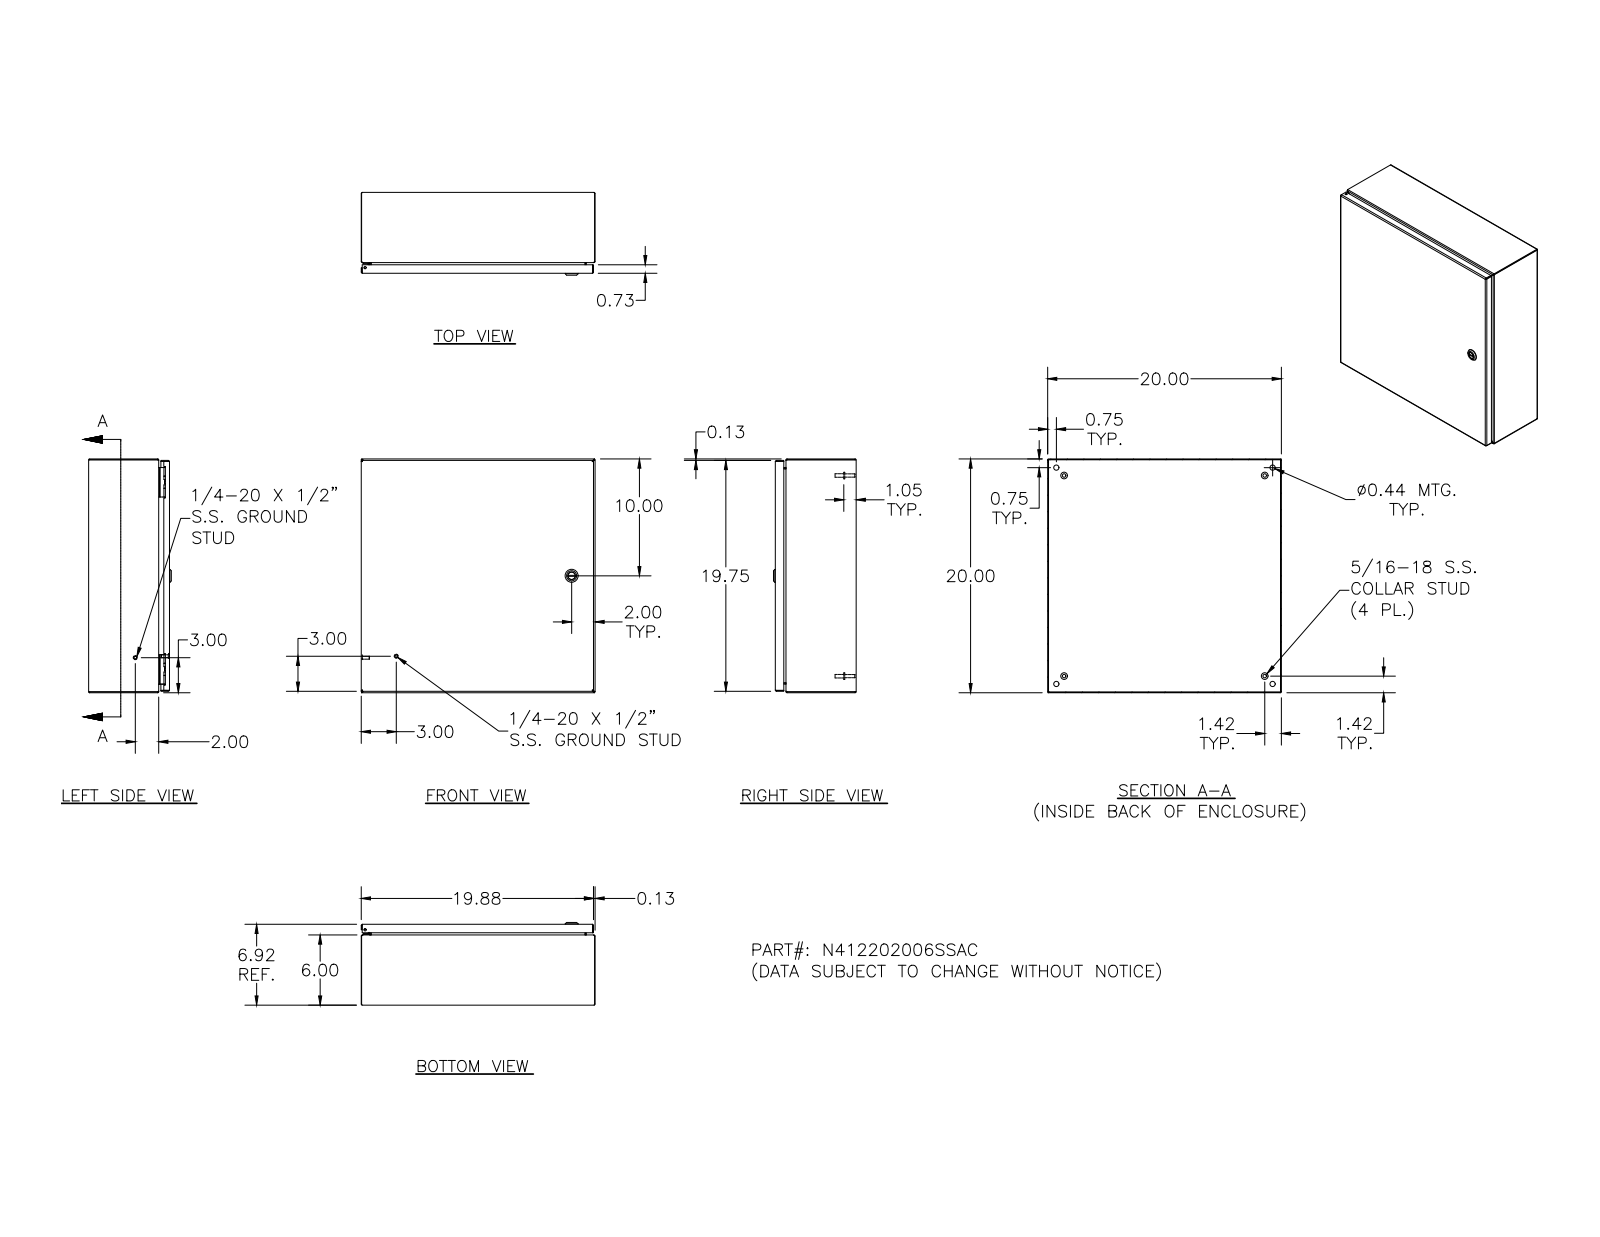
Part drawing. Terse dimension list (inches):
name: N412202006SSAC; N412202006SSACBKP; 388151; N4122020SSACLID (+8 more)
written by: Autodesk Inventor 2011 (AUTOMOTIVE_DESIGN)
unit: in
bodies: 34 solids, 1364 faces (523 planar, 497 cylindrical, 344 other)
size: 20 × 20 × 7.075
volume: 106.9 in³; area: 2 908 in²
holes: 5× ⌀0.188, 4× ⌀0.093, 4× ⌀0.152, 4× ⌀0.167, 4× ⌀0.172, 4× ⌀0.437, 2× ⌀0.156, 1× ⌀0.187, 1× ⌀0.197, 1× ⌀0.315, 1× ⌀0.394, 1× ⌀0.402
bosses: 10× ⌀0.25, 4× ⌀0.563, 4× ⌀0.36, 4× ⌀0.32, 4× ⌀0.3, 4× ⌀0.275, 4× ⌀0.256, 4× ⌀0.164
rounds: 26× R0.05, 18× R0.016, 16× R0.016, 16× R0.09, 14× R0.031, 14× R0.125, 9× R0.02, 8× R0.032
face distances: 0.074, 6.843, 19.926, 6.769, 6.917, 19.852, 20, 5.926, 0.917, 19.187
hole spacings: 16, 0.017, 0.66, 16.008, 18.5, 18.872, 0.019, 0.5
